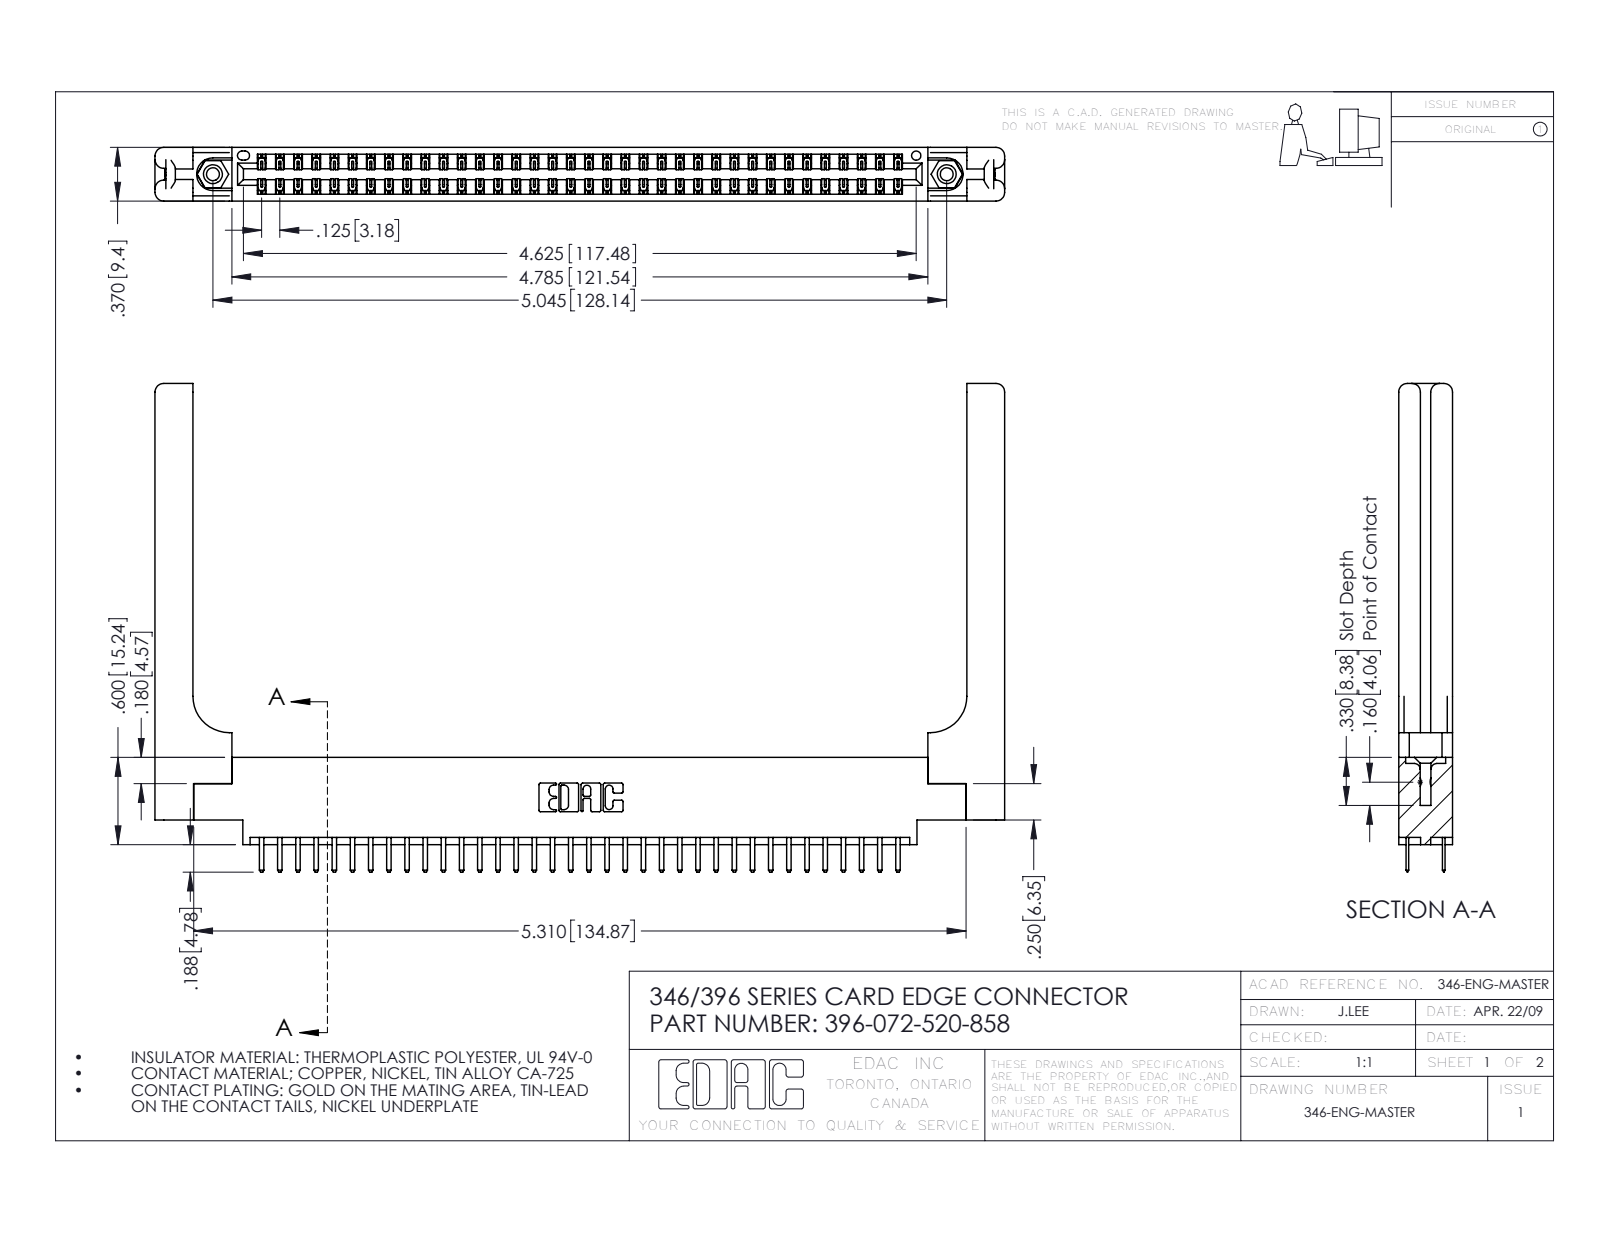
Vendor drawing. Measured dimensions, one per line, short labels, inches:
name: 345-250-001_345-250-001-102; 396-072-520-858; 346 Part_0.170 Offset - 0.156 Dia-TH; 345-292-001_345-293-120 (+1 more)
written by: SolidWorks 2016 (CONFIG_CONTROL_DESIGN)
unit: in
bodies: 77 solids, 4414 faces (2892 planar, 1462 cylindrical, 60 other)
size: 5.841 × 3.358 × 0.37
volume: 1.326 in³; area: 38.05 in²
holes: 2× ⌀0.089, 2× ⌀0.125, 2× ⌀0.156, 1× ⌀0.064
bosses: 2× ⌀0.155
rounds: 108× R0.006, 76× R0.01, 22× R0.01, 16× R0.06, 6× R0.007, 6× R0.031, 3× R0.026, 2× R0.014
face distances: 0.37, 0.048, 0.322, 0.072, 0.148, 0.15, 0.25, 0.298, 0.025, 0.275
hole spacings: 0.246, 4.836, 5.045
